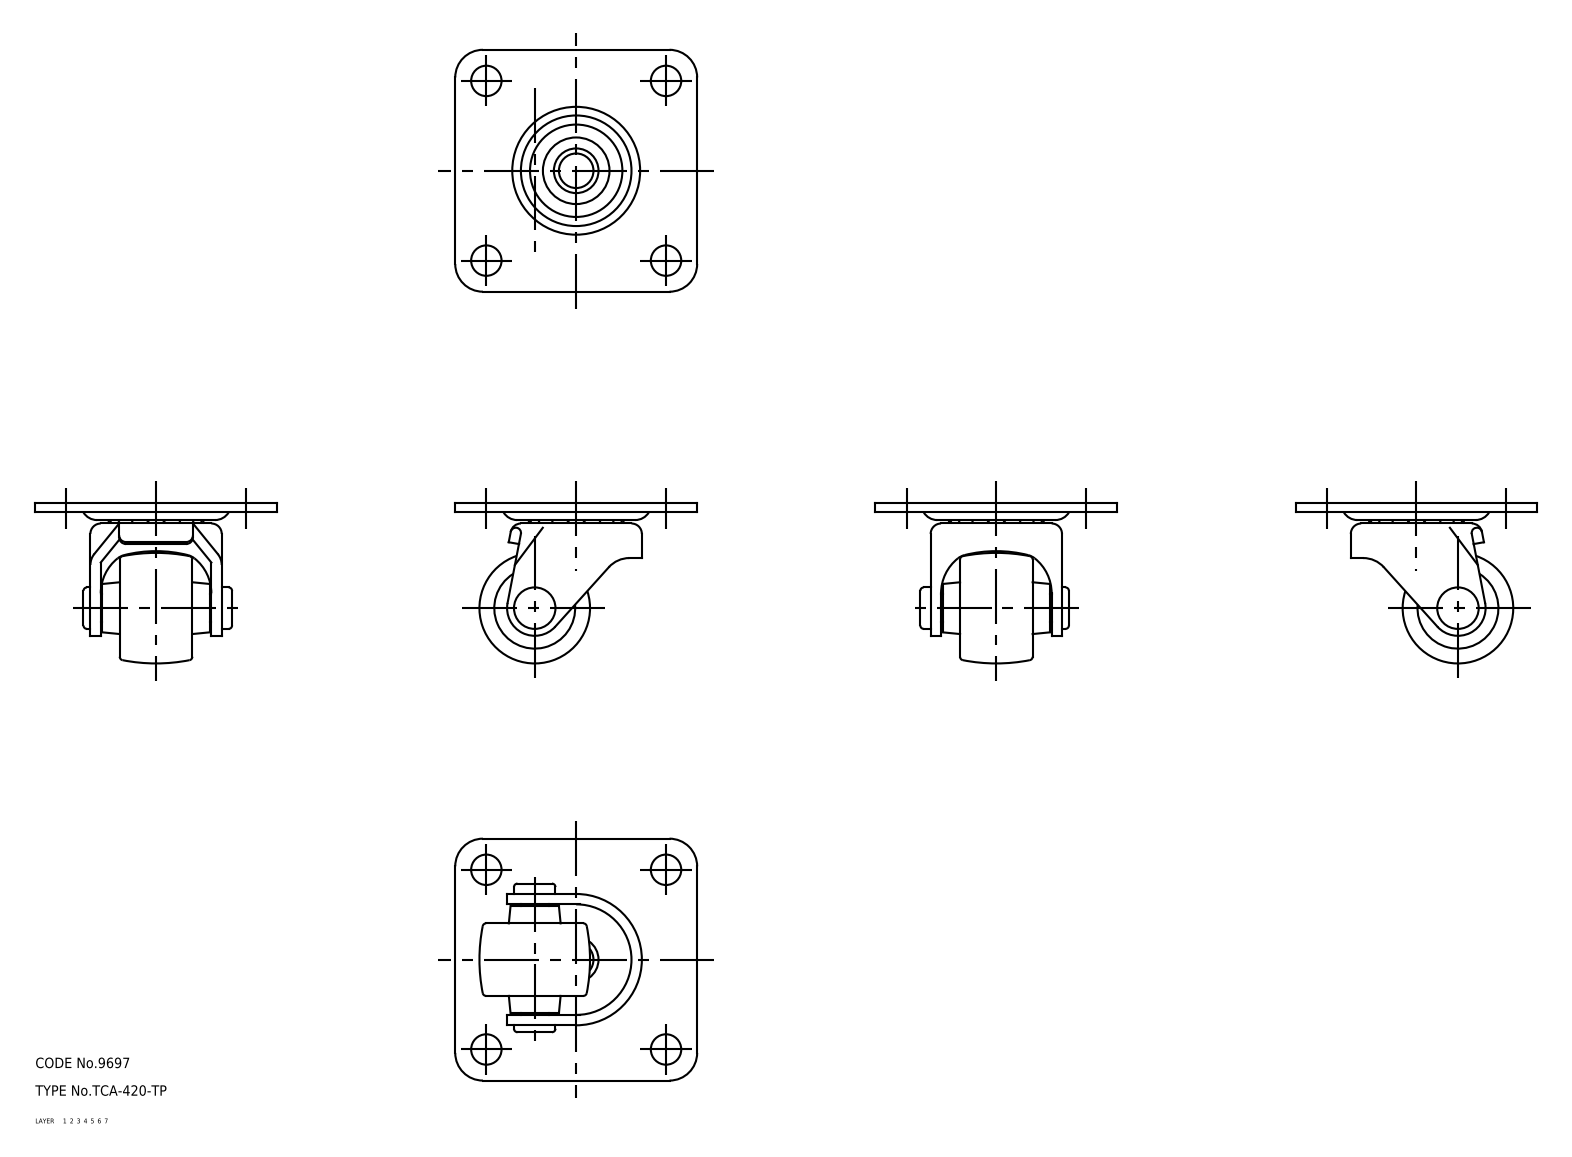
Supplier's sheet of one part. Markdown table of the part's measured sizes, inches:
| quantity | value |
| --- | --- |
| part name | wheel; mounting plate; main shaft; axle (+1 more) |
| STEP written by | CADfix (AUTOMOTIVE_DESIGN) |
| units | inches |
| bodies | 5 solids, 199 faces (0 planar, 0 cylindrical, 199 other) |
| overall size | 2.756 × 2.756 × 1.831 |
| volume | 2.425 in³ |
| surface area | 38.36 in² |
